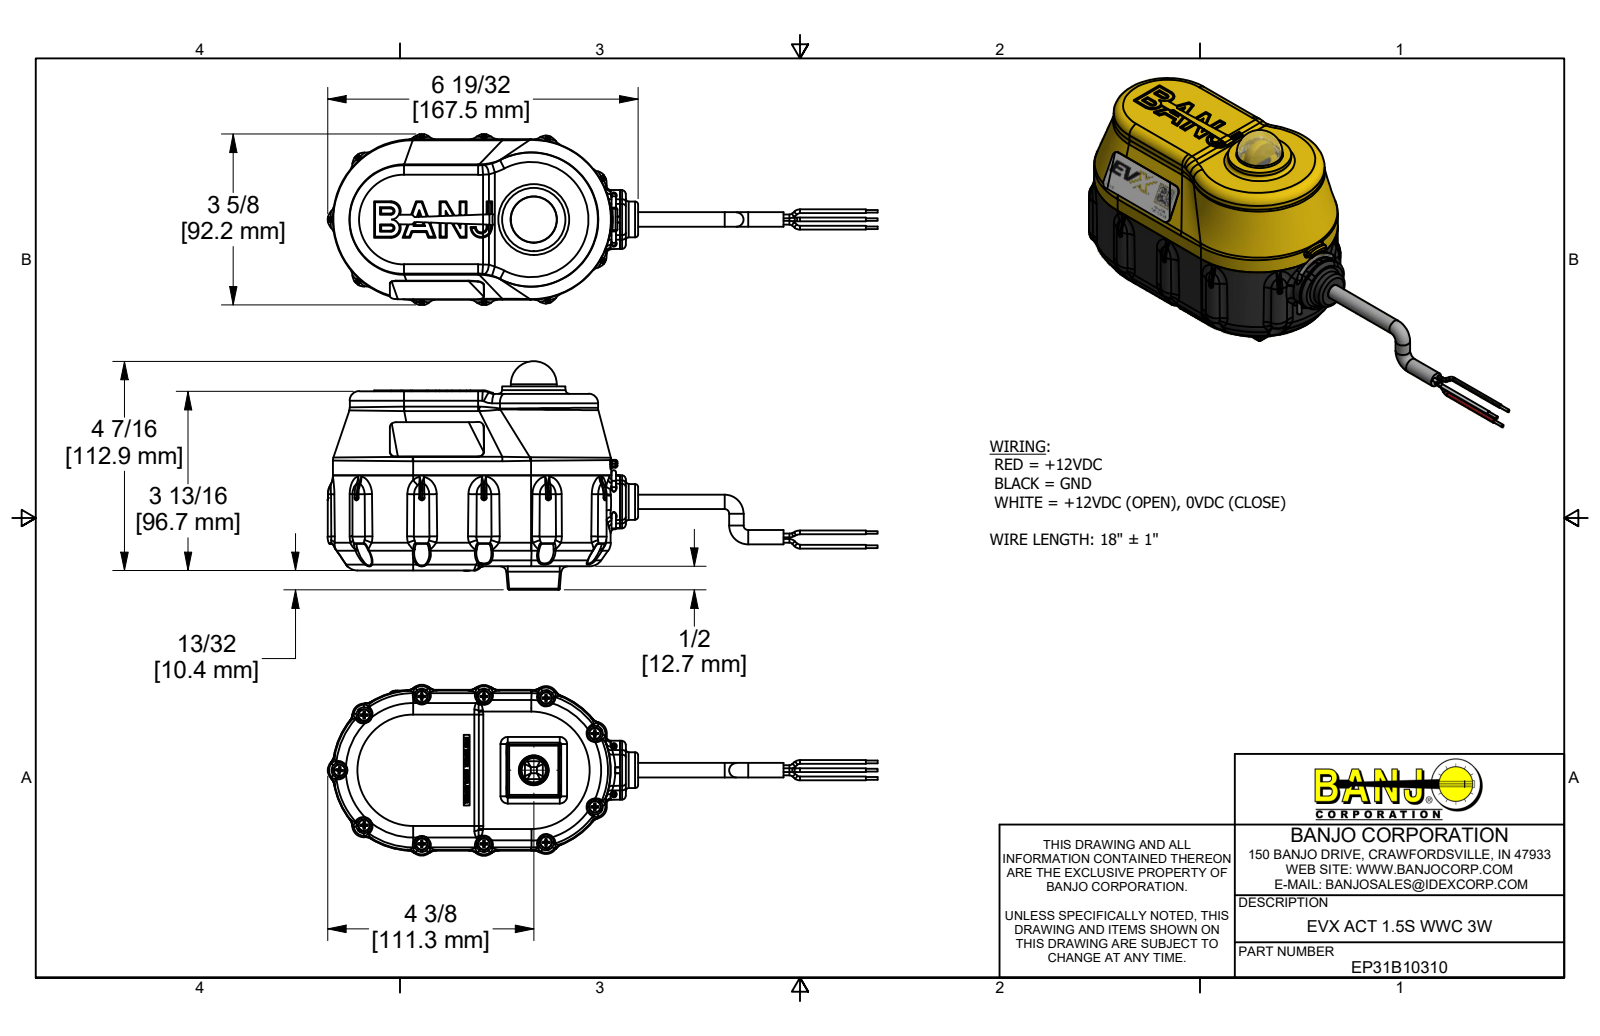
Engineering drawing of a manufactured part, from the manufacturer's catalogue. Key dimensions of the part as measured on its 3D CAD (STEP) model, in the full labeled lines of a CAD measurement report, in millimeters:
Part name (STEP PRODUCT): EP31B10310; B61905PPHS; B632038PM; EP10310 (+8 more)
STEP written by: Autodesk Inventor 2019 (AUTOMOTIVE_DESIGN)
Units: millimetres
Bodies: 73 solids, 10008 faces (2566 planar, 2937 cylindrical, 4505 other)
Overall size (bounding box): 296.8 × 123.3 × 92.2
Volume: 527 300 mm³ · Surface area: 257 600 mm²
Round holes (diameter × count): ⌀2.4 ×11, ⌀3.8 ×11, ⌀2 ×7, ⌀2.7 ×4, ⌀3.2 ×4, ⌀3.5 ×4, ⌀3.8 ×4, ⌀3.8 ×4, ⌀4.3 ×4, ⌀2.7 ×2, ⌀3 ×2, ⌀3.1 ×2
Round bosses / shafts (diameter × count): ⌀6.4 ×17, ⌀2 ×15, ⌀3.6 ×11, ⌀2.7 ×11, ⌀2.2 ×11, ⌀1.5 ×6, ⌀6.9 ×4, ⌀5.6 ×4
Partial cylindrical surfaces — rounded edges, fillets, slot ends (radius × count): R0.3 ×180, R1 ×145, R0.3 ×84, R0.5 ×71, R0.1 ×55, R2 ×28, R0.8 ×26, R2.5 ×22
Main face-to-face distances: 2.5, 65.2, 1.5, 5.4, 3.8, 48.2, 46.6, 42.8, 14.5, 16
Hole centre spacings: 32.6, 45.1, 68.3, 69.3, 96.2, 12.4, 17, 24.2
